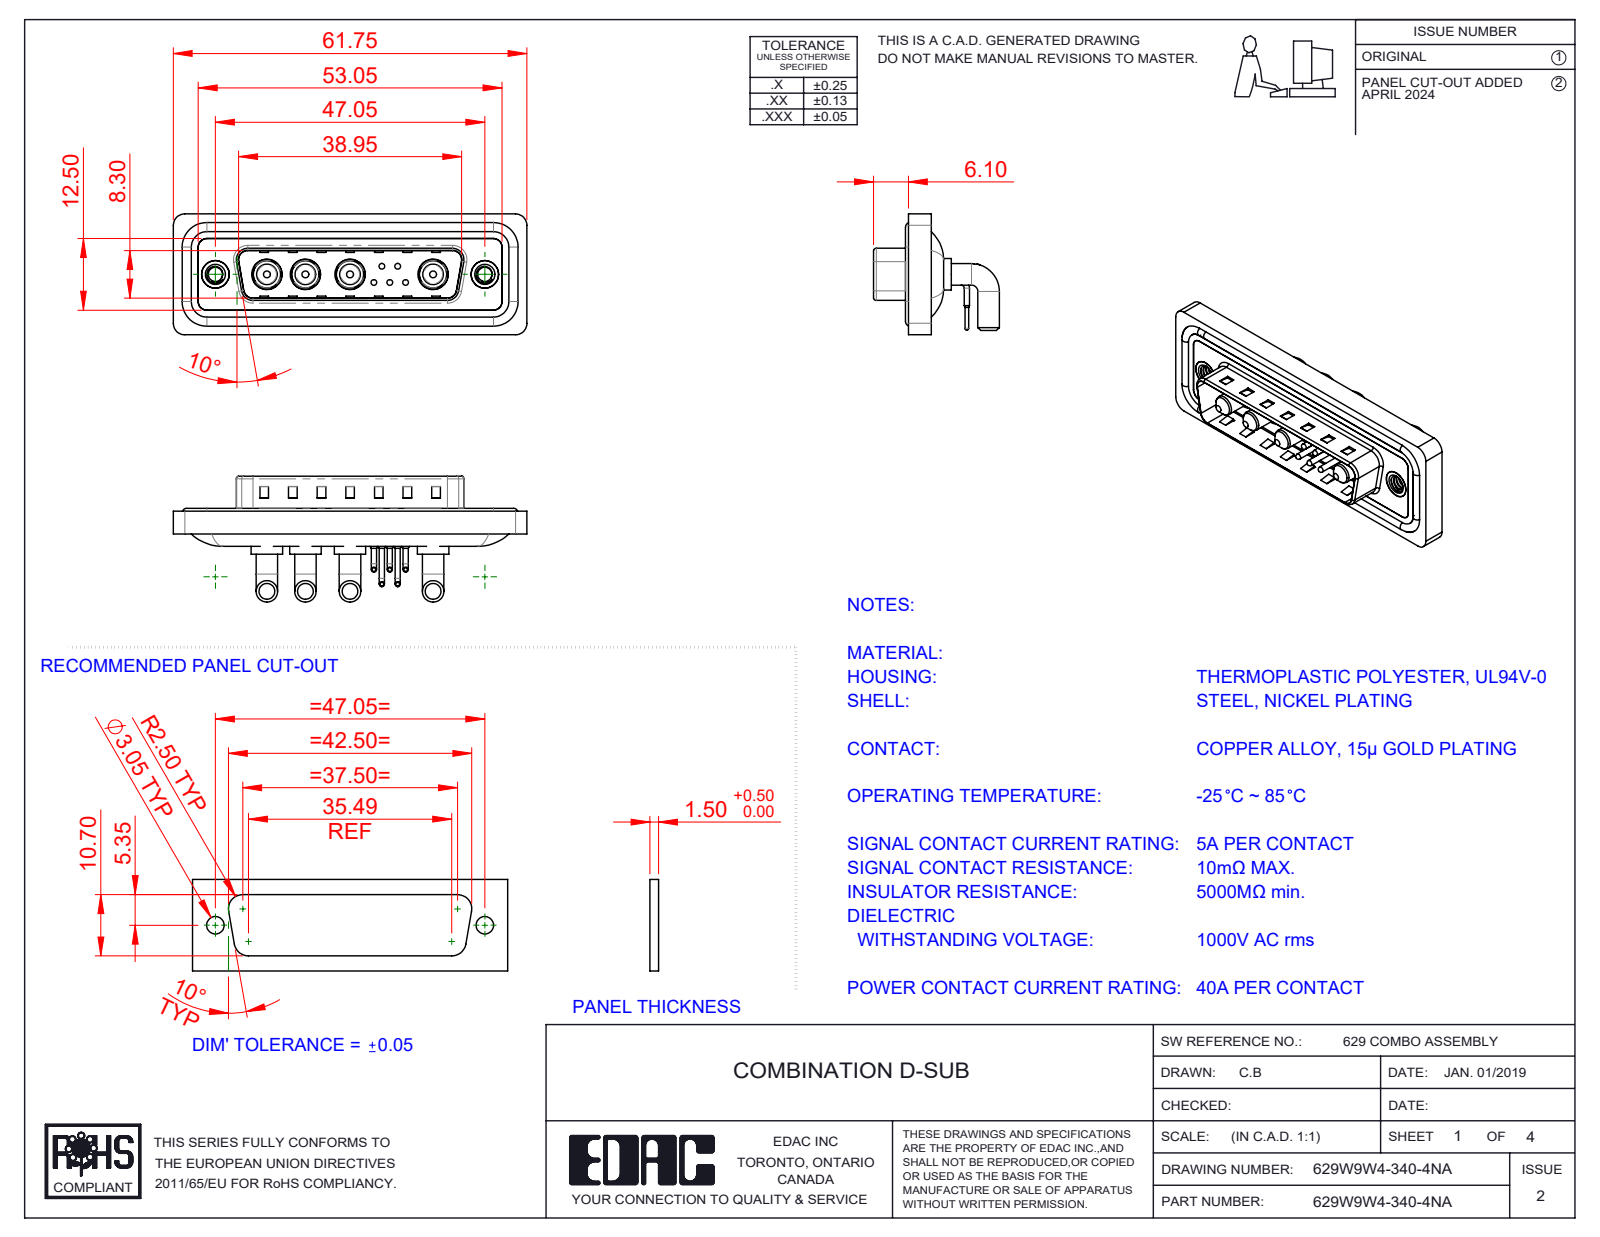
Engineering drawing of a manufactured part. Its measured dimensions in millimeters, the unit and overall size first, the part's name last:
Units: millimetres
Overall size (bounding box): 61.75 × 21.98 × 21.1
Round holes (diameter × count): ⌀0.75 ×5, ⌀1.6 ×5, ⌀2 ×5, ⌀4.85 ×4, ⌀5.3 ×4, ⌀2.5 ×2, ⌀4 ×2, ⌀4.8 ×2, ⌀5 ×2
Round bosses / shafts (diameter × count): ⌀0.9 ×10, ⌀3.75 ×8, ⌀1.5 ×5, ⌀1 ×5, ⌀0.65 ×5, ⌀5.5 ×4, ⌀5.2 ×4, ⌀4.75 ×4
Partial cylindrical surfaces — rounded edges, fillets, slot ends (radius × count): R1.5 ×18, R2 ×18, R0.5 ×8, R1.6 ×8, R1.01 ×5, R0.25 ×4, R0.6 ×4, R0.65 ×4
Main face-to-face distances: 0.4, 2.9, 0.8, 4.1, 1.1, 4.5, 2.1, 1.6, 3.1, 6
Hole centre spacings: 3.16, 2.77, 5.04, 14.5, 2.78, 4.4, 4.41, 5
Volume: 8 000 mm³ · Surface area: 12 556 mm²
Bodies: 20 solids, 1199 faces (569 planar, 450 cylindrical, 180 other)
Part name (STEP PRODUCT): 629Combo Shell Front_25 Contacts; 629Combo Housing_9W4; 629Combo Waterproof Housing_25 Contacts; 629Combo Contact Row 2 (+5 more)
STEP written by: SolidWorks 2023 (CONFIG_CONTROL_DESIGN)
